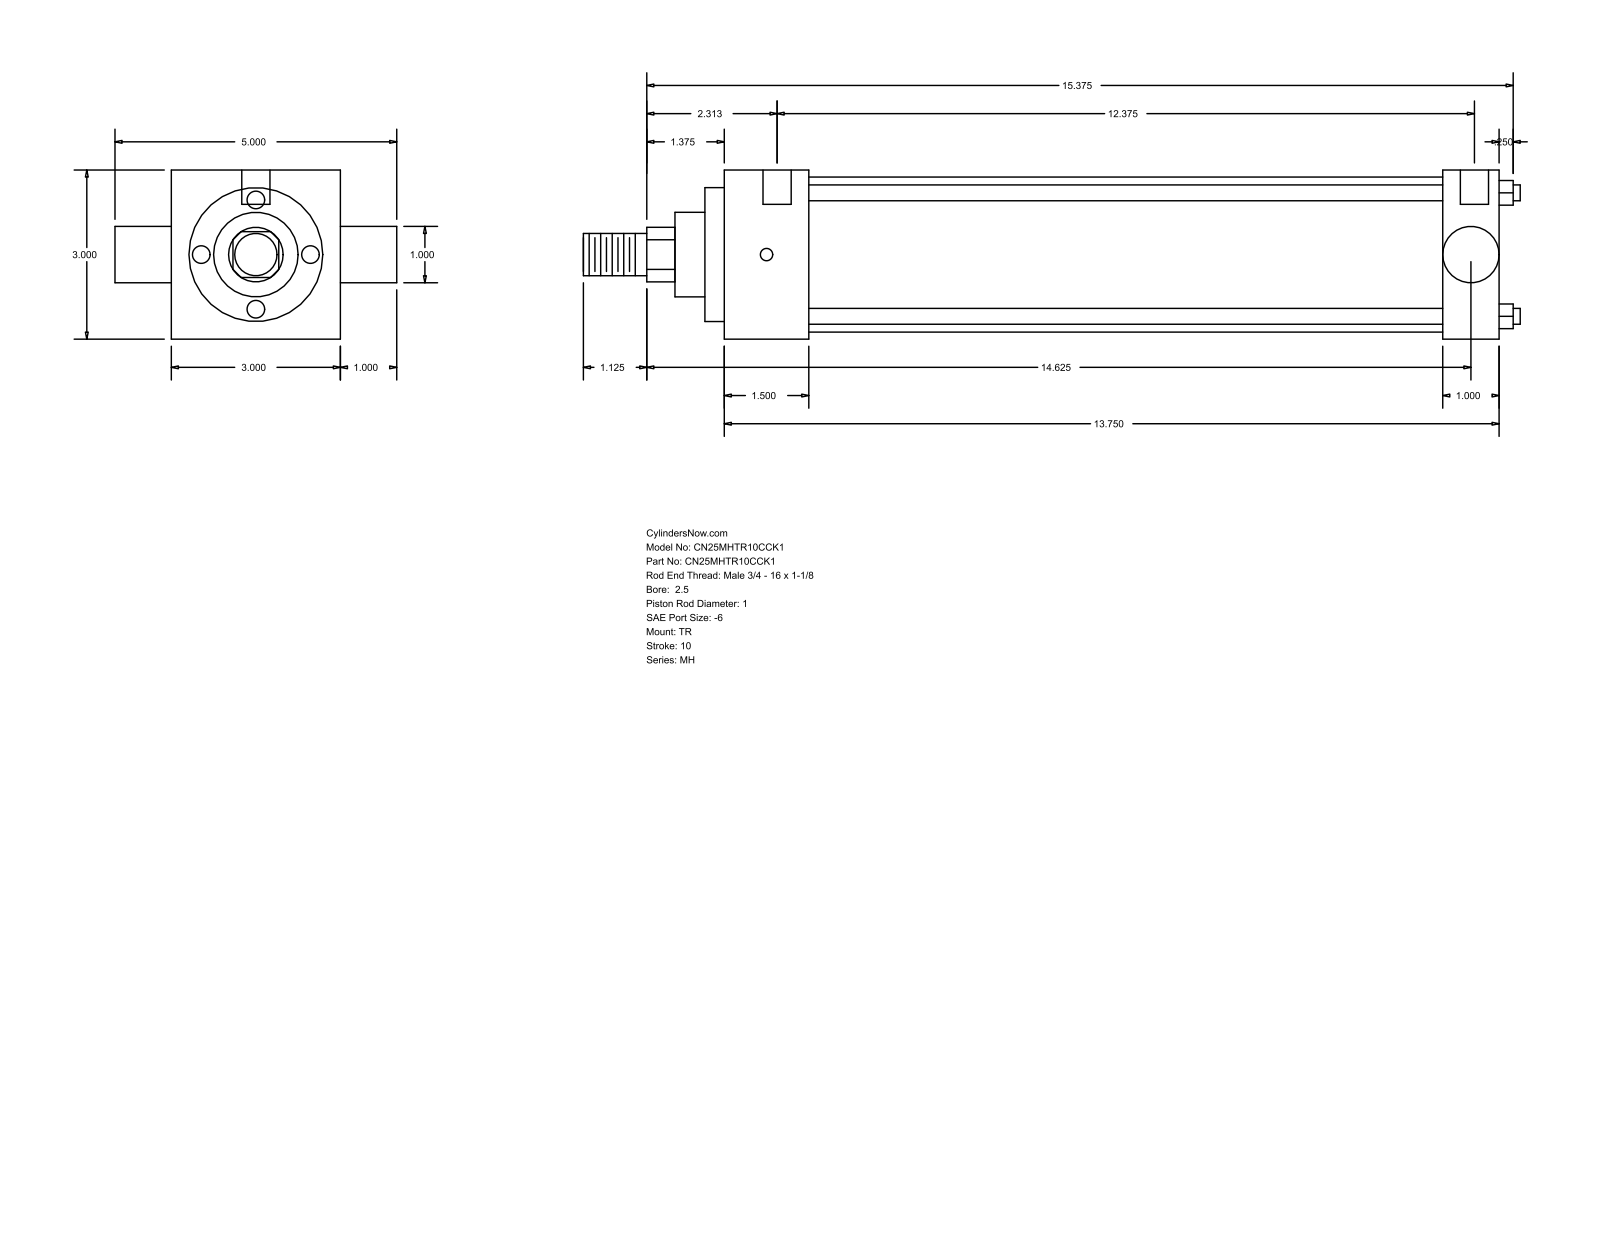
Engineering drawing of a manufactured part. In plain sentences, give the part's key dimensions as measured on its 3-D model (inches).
The part is named "MH_TR__0250_1". Its 3-D file was written by "GSSL Pune (CONFIG_CONTROL_DESIGN)". It is 0 solids with 86 faces: 61 planar, 25 cylindrical and 0 other. Overall it measures 16.625 by 5 by 3 inches. Round holes: 3 of diameter 0.219, 2 of diameter 0.5. Round bosses or shafts: 4 of diameter 0.281, 1 of diameter 2.75, 1 of diameter 2.375, 1 of diameter 1.5, 1 of diameter 1, 1 of diameter 0.998, 1 of diameter 0.75. Partial cylindrical surfaces (rounded edges, fillets, slot ends): 1 of radius 0.484. The main face-to-face distances are 3, 13.75, 1.5, 12.25, 12.75, 11.25, 1, 0.344, 1.844, 13.094. The hole center spacings are 0.125, 0.187, 12.375, 12.5, 12.562, 12.687.
